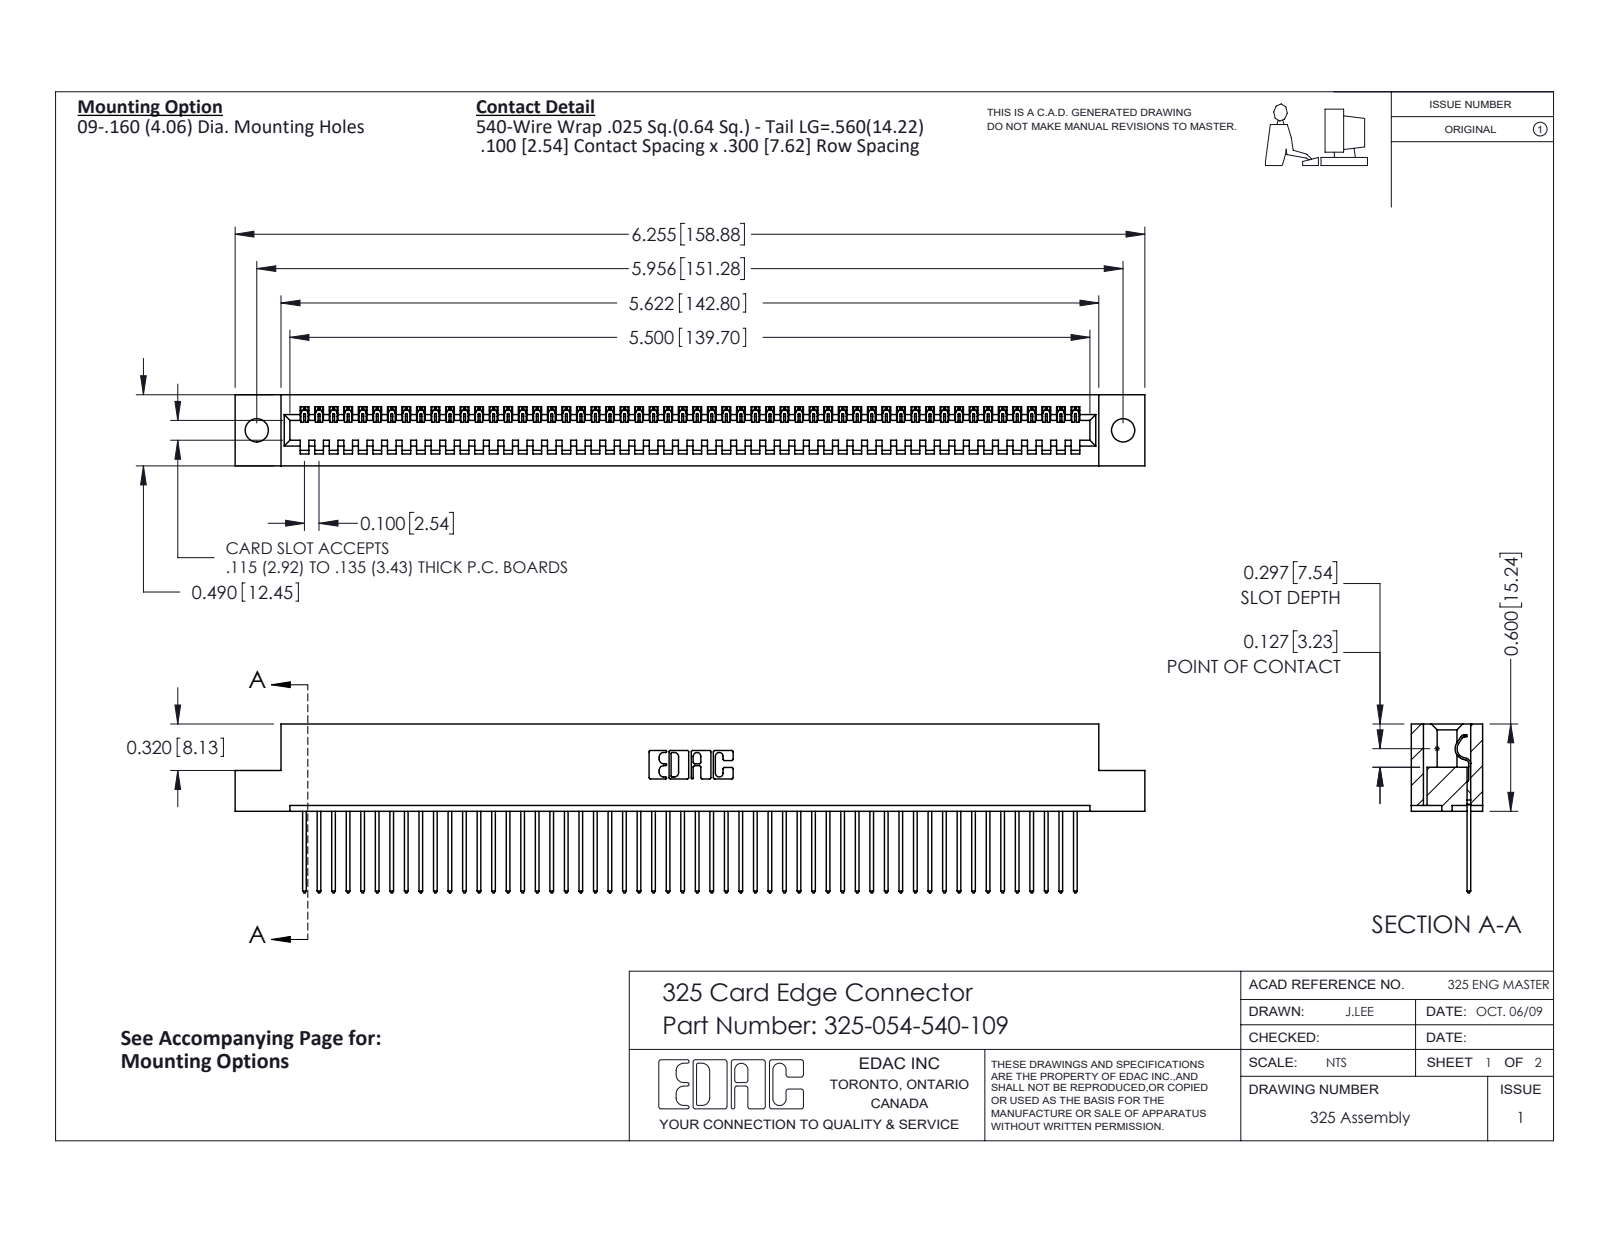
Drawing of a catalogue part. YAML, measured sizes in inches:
part_name: "325-292-001_325-293-140; 325-054-540-109; 325 Part_.160 TH"
step_written_by: "SolidWorks 2016 (CONFIG_CONTROL_DESIGN)"
units: inches
bodies: {solids: 55, faces: 3246, planar: 2338, cylindrical: 908, other: 0}
overall_size: [6.255, 1.16, 0.49]
volume: 1.227
surface_area: 35.04
round_holes:
  - {diameter: 0.16, count: 2}
partial_cylinders:
  - {radius: 0.006, count: 108}
  - {radius: 0.01, count: 108}
  - {radius: 0.01, count: 22}
  - {radius: 0.007, count: 6}
  - {radius: 0.031, count: 6}
  - {radius: 0.026, count: 3}
  - {radius: 0.014, count: 1}
  - {radius: 0.022, count: 1}
face_to_face_distances: [0.083, 0.407, 0.3, 0.49, 0.107, 0.383, 0.025, 0.325, 0.56, 0.263]
hole_center_spacings: [5.956]
